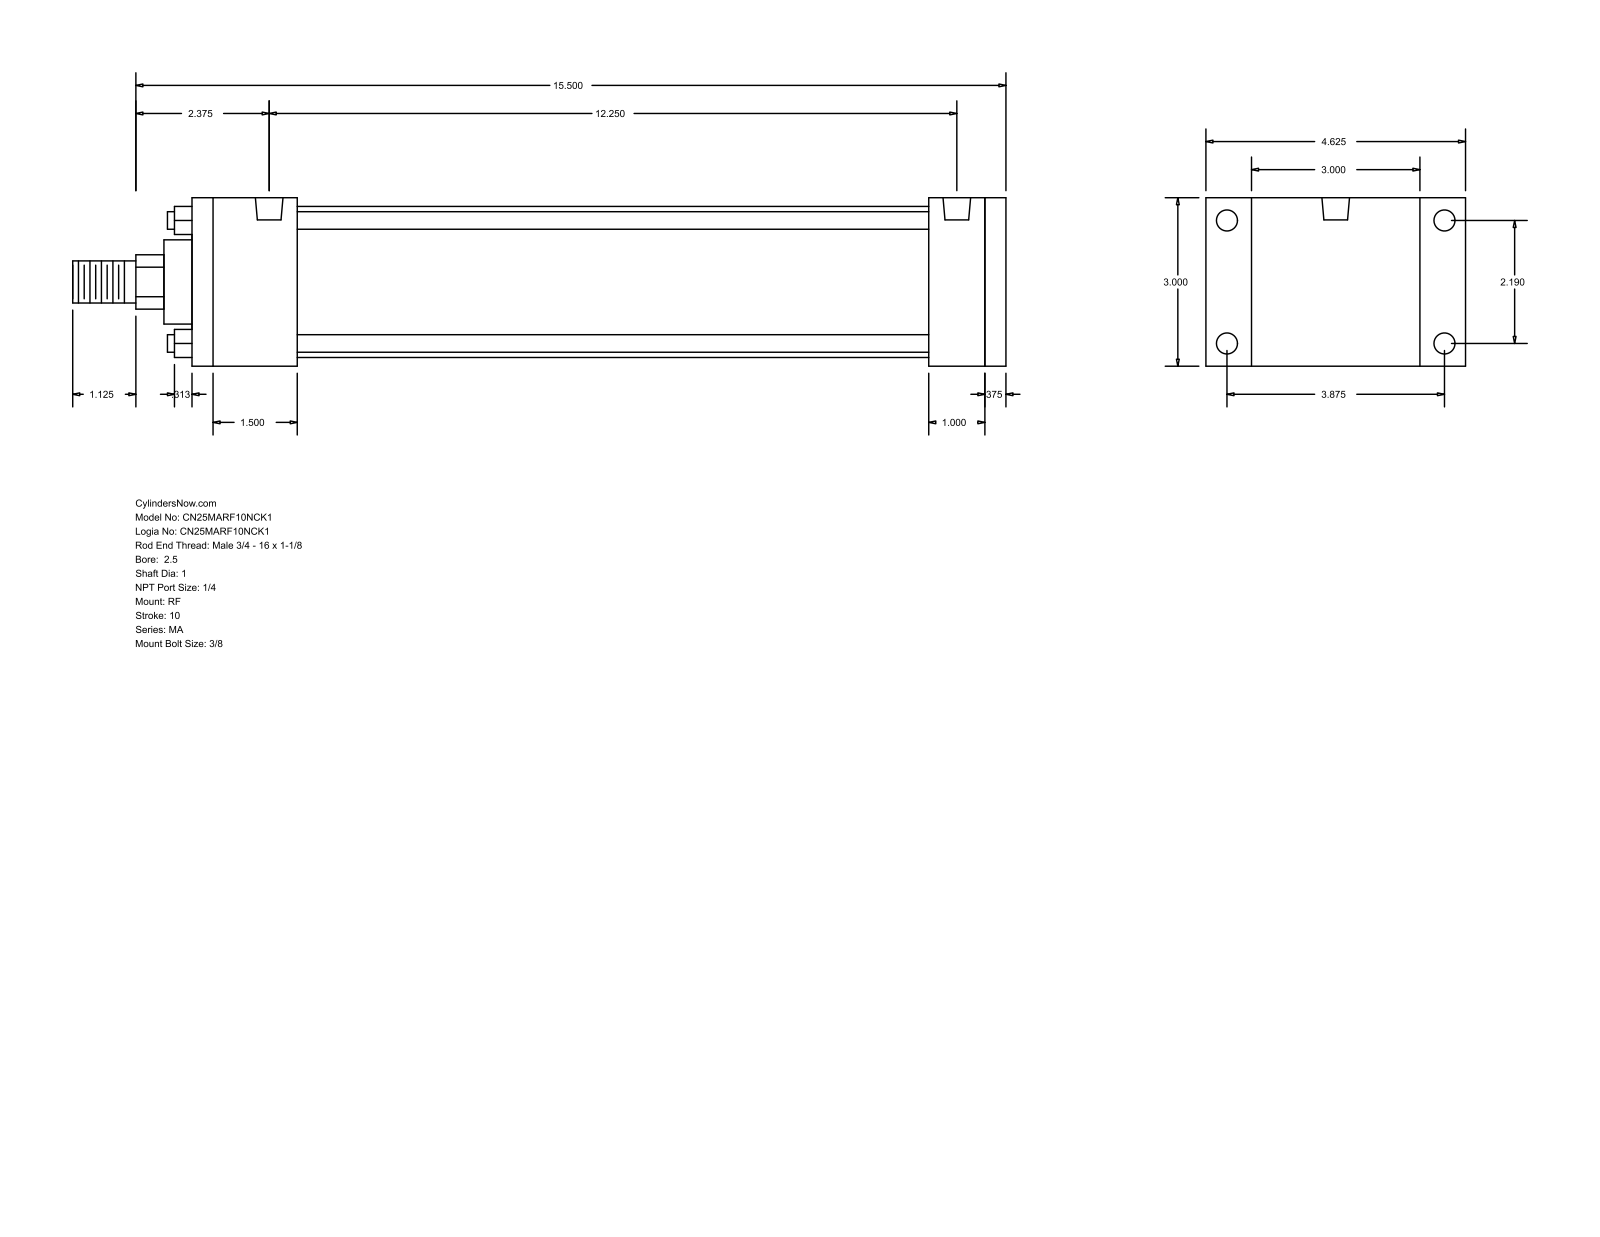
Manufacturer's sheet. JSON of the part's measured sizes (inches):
{"part_name": "MA_RF__0250_1", "step_written_by": "GSSL Pune (CONFIG_CONTROL_DESIGN)", "units": "inches", "bodies": {"solids": 0, "faces": 92, "planar": 64, "cylindrical": 28, "other": 0}, "overall_size": [16.625, 4.625, 3], "round_holes": [[0.313, 4], [0.375, 4], [0.492, 2]], "round_bosses_or_shafts": [[0.313, 4], [2.69, 1], [1.5, 1], [1, 1], [0.75, 1]], "partial_cylinders_radius": [[0.484, 1]], "face_to_face_distances": [3, 14.5, 14.125, 0.375, 1.875, 13.125, 11.25, 12.25, 12.625, 1], "hole_center_spacings": [2.19, 3.875, 4.451, 12.25]}
